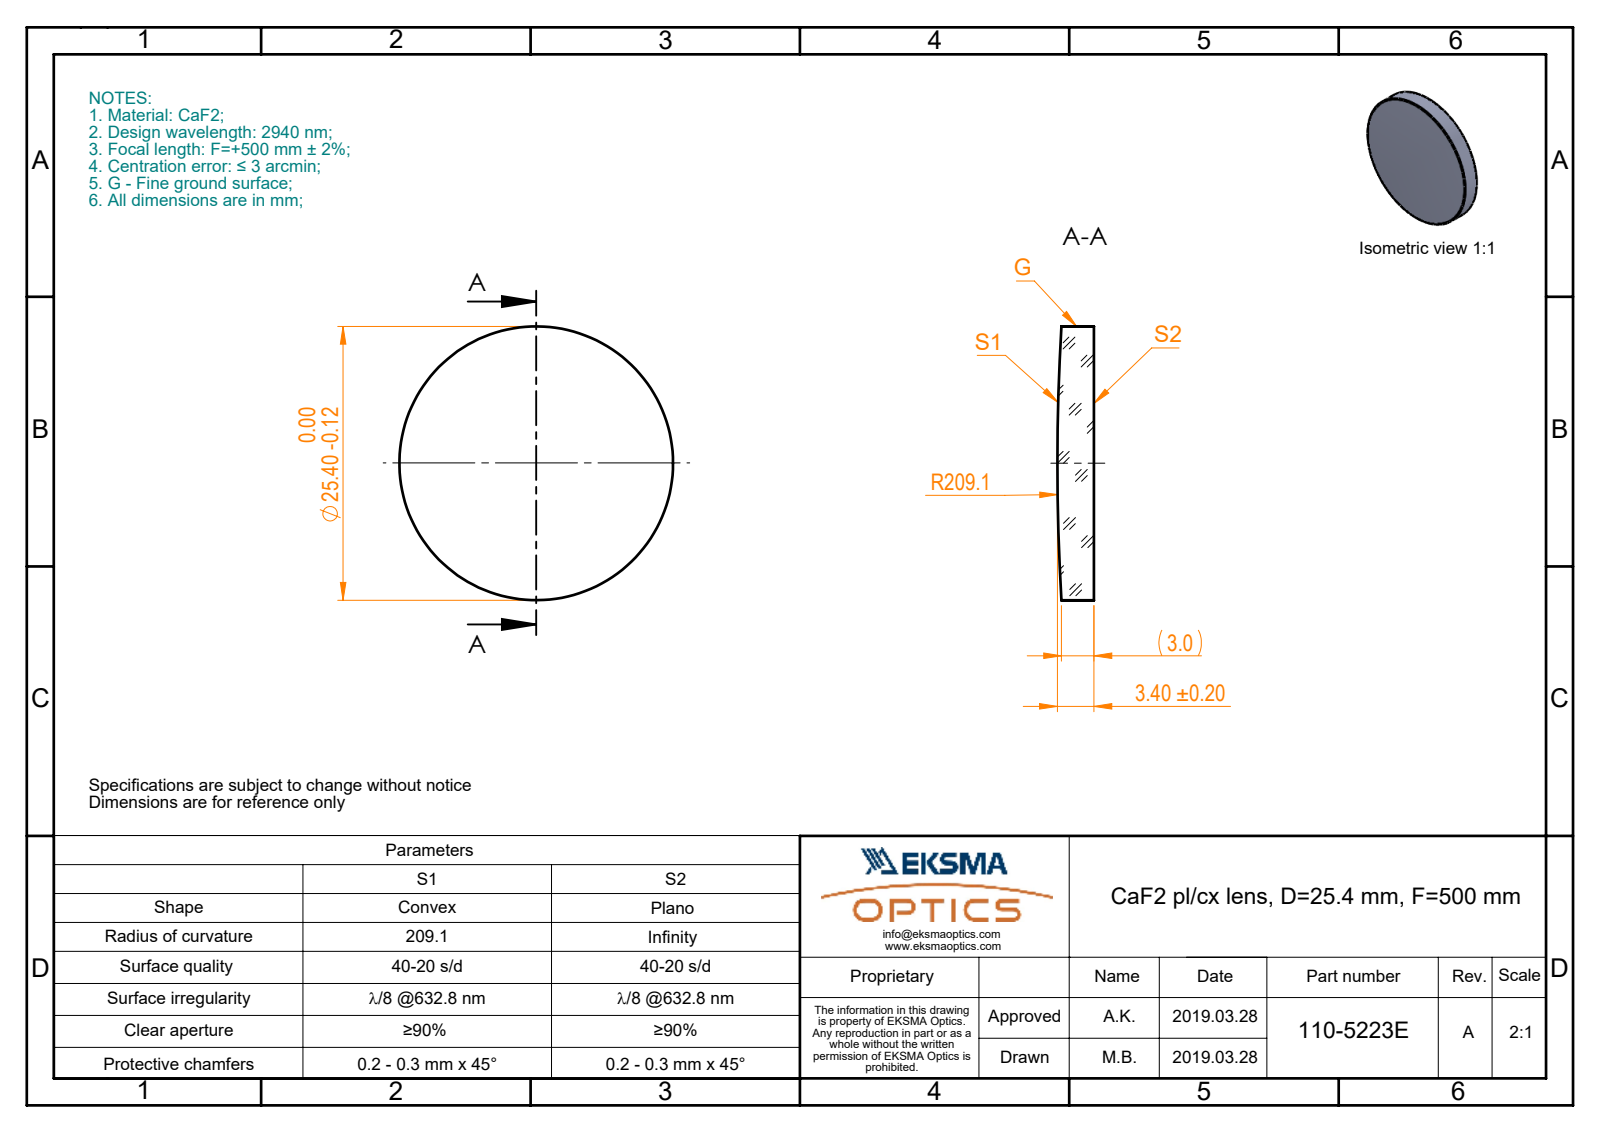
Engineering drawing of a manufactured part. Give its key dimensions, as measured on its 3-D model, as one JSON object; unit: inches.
{"part_name": "110-5223E CaF2 pl-cx 25.4 F500", "step_written_by": "SolidWorks 2017 (CONFIG_CONTROL_DESIGN)", "units": "inches", "bodies": {"solids": 1, "faces": 5, "planar": 1, "cylindrical": 2, "other": 2}, "overall_size": [1, 1, 0.134], "volume_in3": 0.099, "surface_area_in2": 1.944, "round_bosses_or_shafts": [[1, 1]]}
